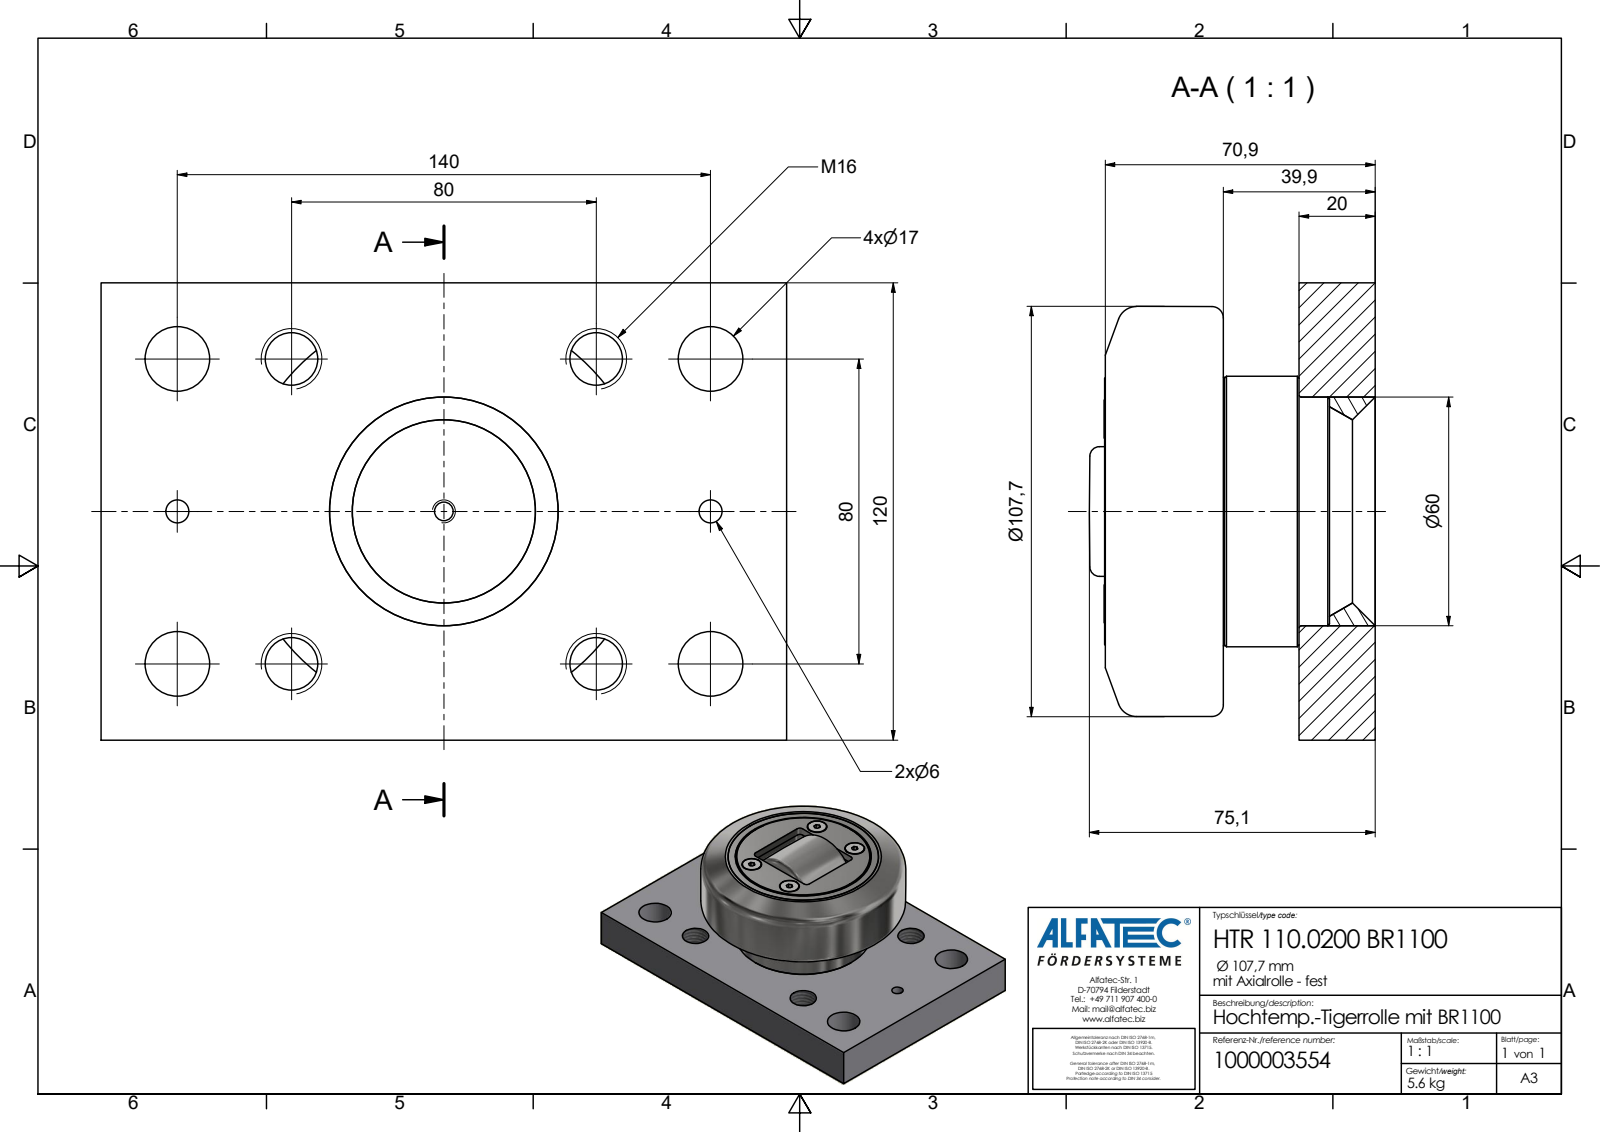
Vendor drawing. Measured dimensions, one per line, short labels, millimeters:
name: HTR 110.0200 BR1100_Kontur
written by: Autodesk Inventor 2020 (AP242_MANAGED_MODEL_BASED_3D_ENGINEERING_MIM_LF)
unit: mm
bodies: 1 solid, 83 faces (49 planar, 20 cylindrical, 14 other)
size: 180 × 120 × 75.1
volume: 753 672 mm³; area: 84 245 mm²
holes: 4× ⌀13.84, 4× ⌀17, 2× ⌀6
bosses: 4× ⌀10, 1× ⌀71, 1× ⌀70.5
rounds: 4× R2
face distances: 20, 39.9, 19.9, 120, 180, 71.1, 51.1, 31.2, 31, 70.9
hole spacings: 80, 30, 40, 50, 85.44, 110, 117.05, 136.01
